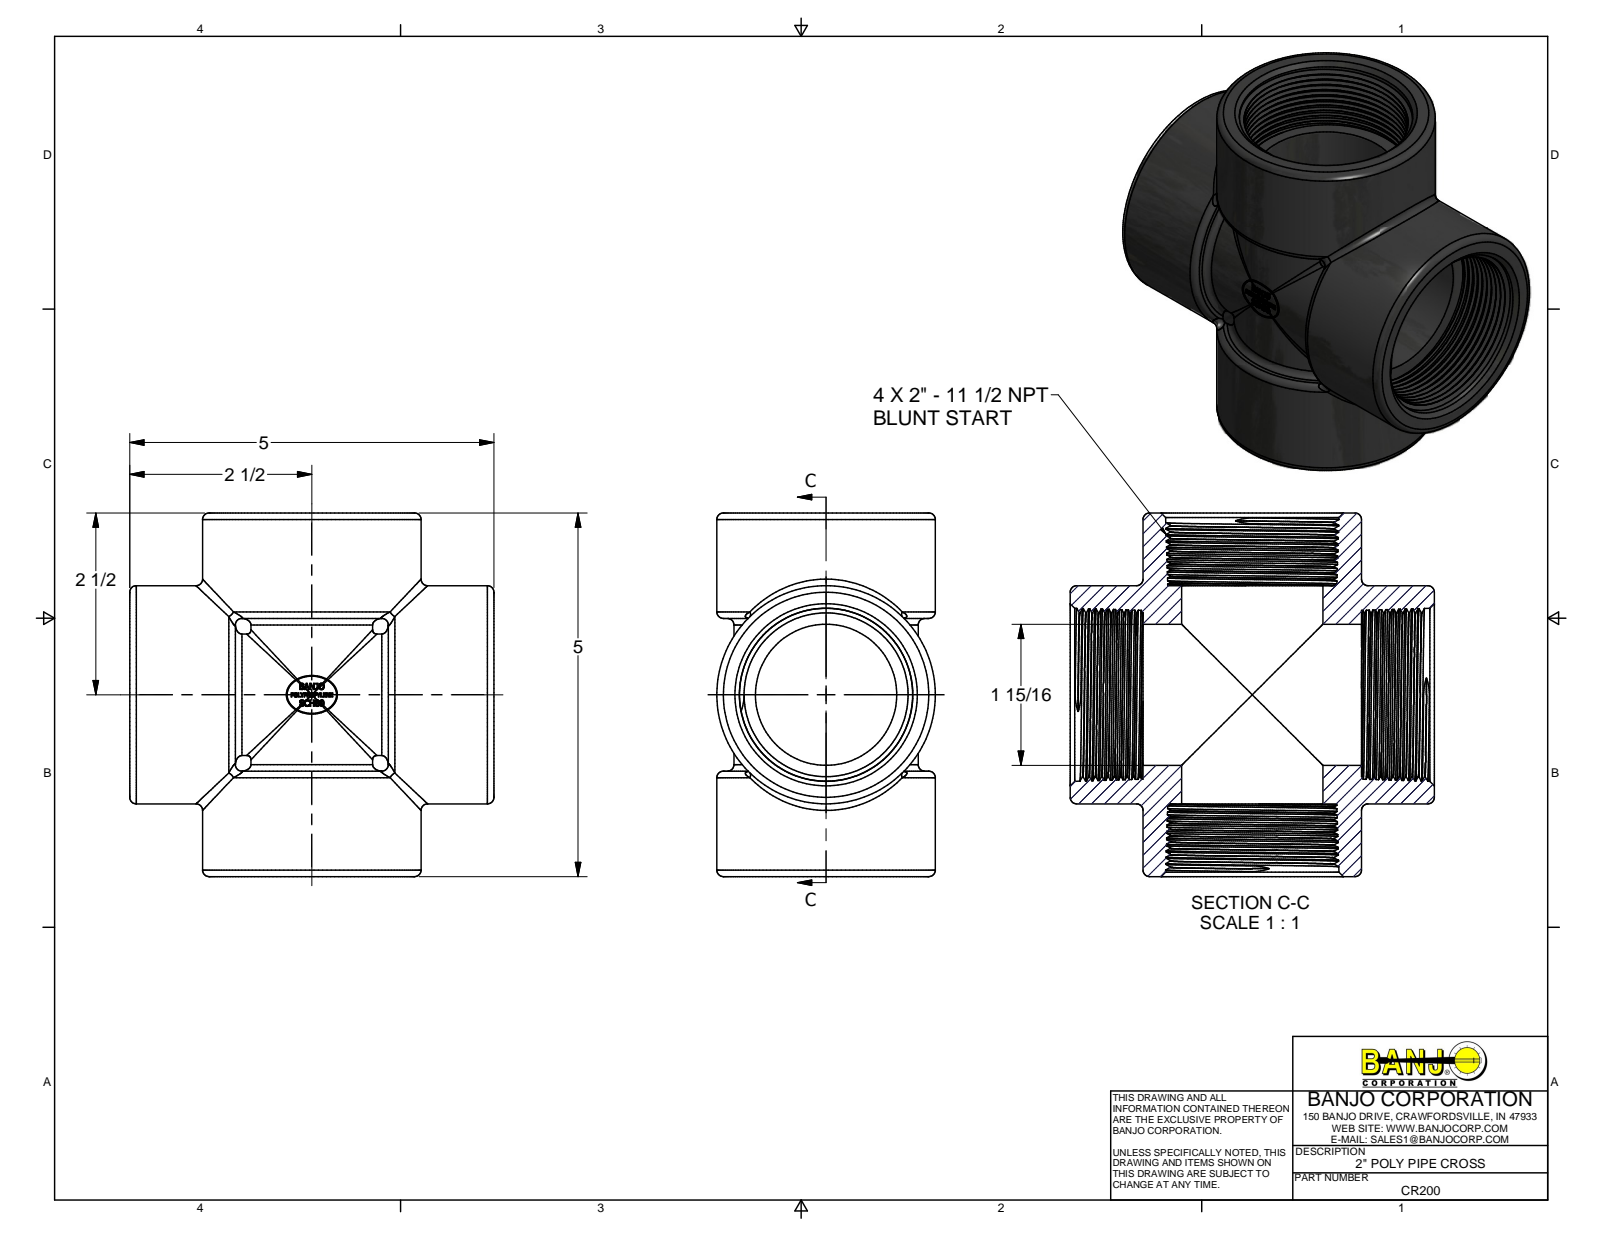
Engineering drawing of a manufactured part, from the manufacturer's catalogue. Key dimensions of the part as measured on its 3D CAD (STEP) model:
Part name (STEP PRODUCT): CR200
STEP written by: Autodesk Inventor 2014 (AUTOMOTIVE_DESIGN)
Units: millimetres
Bodies: 1 solid, 573 faces (183 planar, 83 cylindrical, 307 other)
Overall size (bounding box): 127 × 127 × 76.2
Volume: 342 996 mm³ · Surface area: 93 508 mm²
Round holes (diameter × count): ⌀49.28 ×2
Round bosses / shafts (diameter × count): ⌀76.2 ×2
Partial cylindrical surfaces — rounded edges, fillets, slot ends (radius × count): R16.73 ×2, R32.13 ×2, R32.38 ×2
Main face-to-face distances: 25.4, 101.6, 127, 76.2, 36.83, 90.17, 11.43, 64.77, 53.34, 48.26
